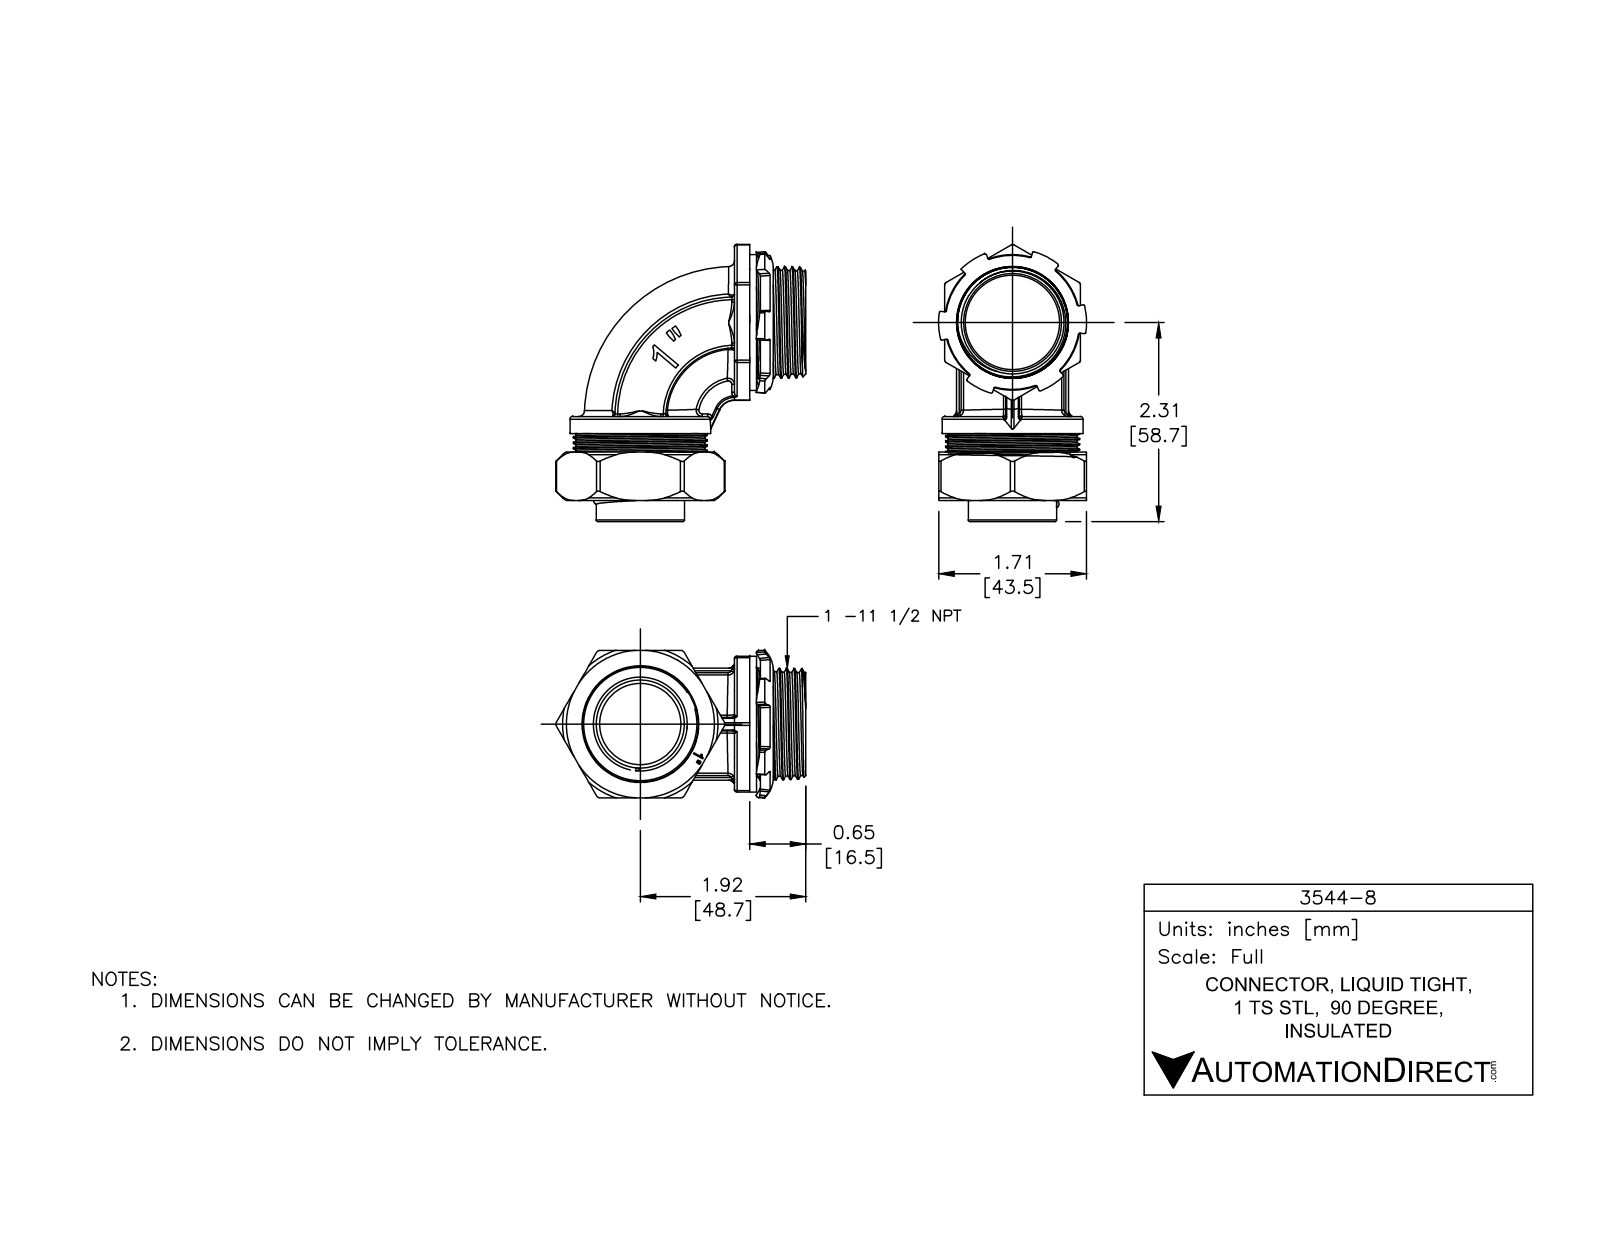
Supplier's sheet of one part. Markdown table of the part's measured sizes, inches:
| quantity | value |
| --- | --- |
| part name | 3424 90DEG BODY; 3404 GLAND RING_1; 3404 FERRULE_installed; 3404 LOCK NUT (+4 more) |
| STEP written by | SolidWorks 2014 (AUTOMOTIVE_DESIGN) |
| units | inches |
| bodies | 7 solids, 626 faces (215 planar, 135 cylindrical, 276 other) |
| overall size | 3.217 × 2.959 × 1.717 |
| volume | 2.114 in³ |
| surface area | 63.03 in² |
| round holes (diameter × count) | 1.102 × 2, 0.15 × 1, 0.943 × 1, 0.985 × 1, 1.095 × 1, 1.215 × 1, 1.331 × 1, 1.335 × 1, 1.354 × 1, 1.386 × 1, 1.516 × 1 |
| round bosses / shafts (diameter × count) | 1.634 × 1, 1.575 × 1, 1.555 × 1, 1.496 × 1, 1.37 × 1, 1.161 × 1, 1.024 × 1, 0.983 × 1 |
| partial cylindrical surfaces (radius × count) | 0.031 × 21, 0.01 × 8, 0.05 × 6, 0.021 × 2, 0.046 × 2, 0.005 × 1, 0.013 × 1, 0.019 × 1 |
| main face-to-face distances | 1.713, 0.207, 1.506, 1.299, 0.813, 0.079, 0.571, 0.709, 0.177, 0.256 |
| hole center spacings | 0.775 |
